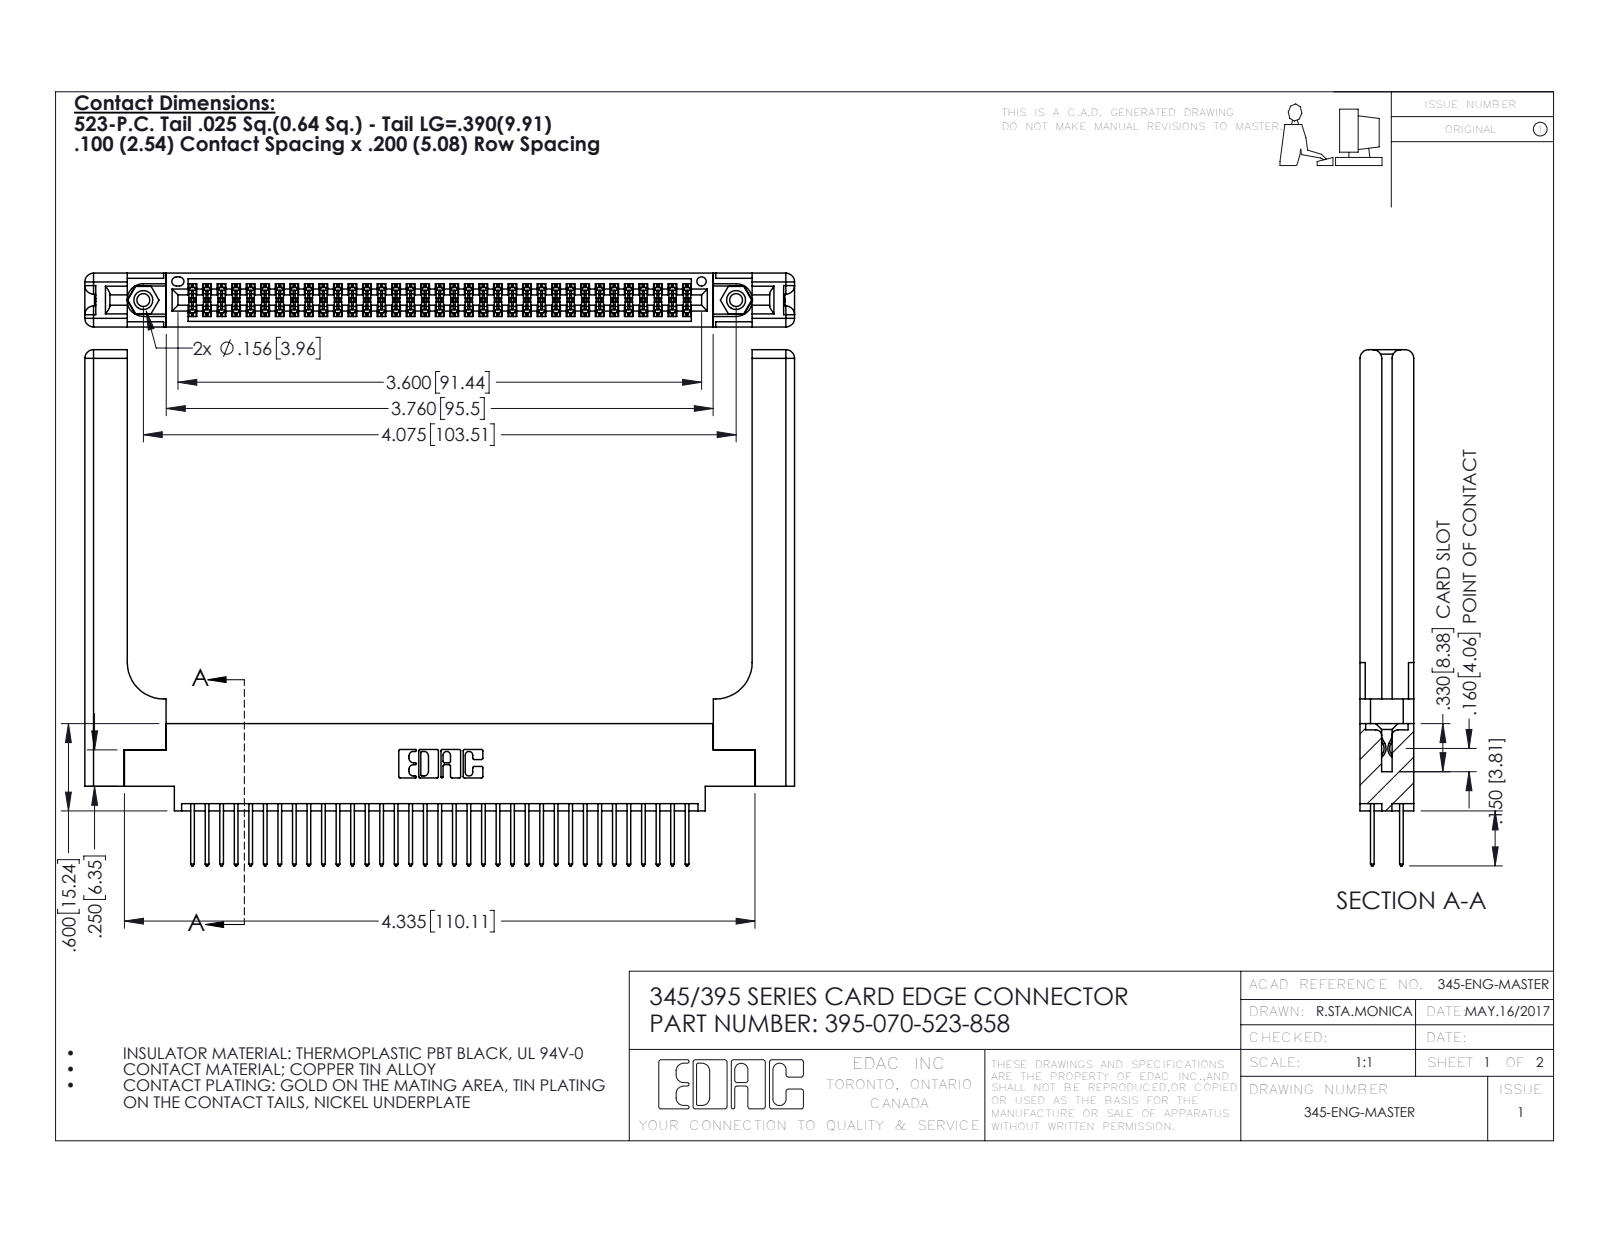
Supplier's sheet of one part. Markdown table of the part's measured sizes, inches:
| quantity | value |
| --- | --- |
| part name | 345-250-001_345-250-001-102; 345-292-001_345-293-123; 395-070-523-858; 345-220-058_345-220-058 (+1 more) |
| STEP written by | SolidWorks 2016 (CONFIG_CONTROL_DESIGN) |
| units | inches |
| bodies | 75 solids, 3886 faces (2542 planar, 1284 cylindrical, 60 other) |
| overall size | 4.879 × 3.547 × 0.37 |
| volume | 1.25 in³ |
| surface area | 36.35 in² |
| round holes (diameter × count) | 0.089 × 2, 0.125 × 2, 0.156 × 2, 0.064 × 1 |
| round bosses / shafts (diameter × count) | 0.155 × 2 |
| partial cylindrical surfaces (radius × count) | 0.006 × 105, 0.01 × 70, 0.01 × 22, 0.06 × 16, 0.007 × 6, 0.031 × 6, 0.026 × 3, 0.014 × 2 |
| main face-to-face distances | 0.072, 0.37, 0.298, 0.098, 0.272, 0.025, 0.2, 0.225, 0.175, 0.148 |
| hole center spacings | 0.27, 3.839, 4.075 |
